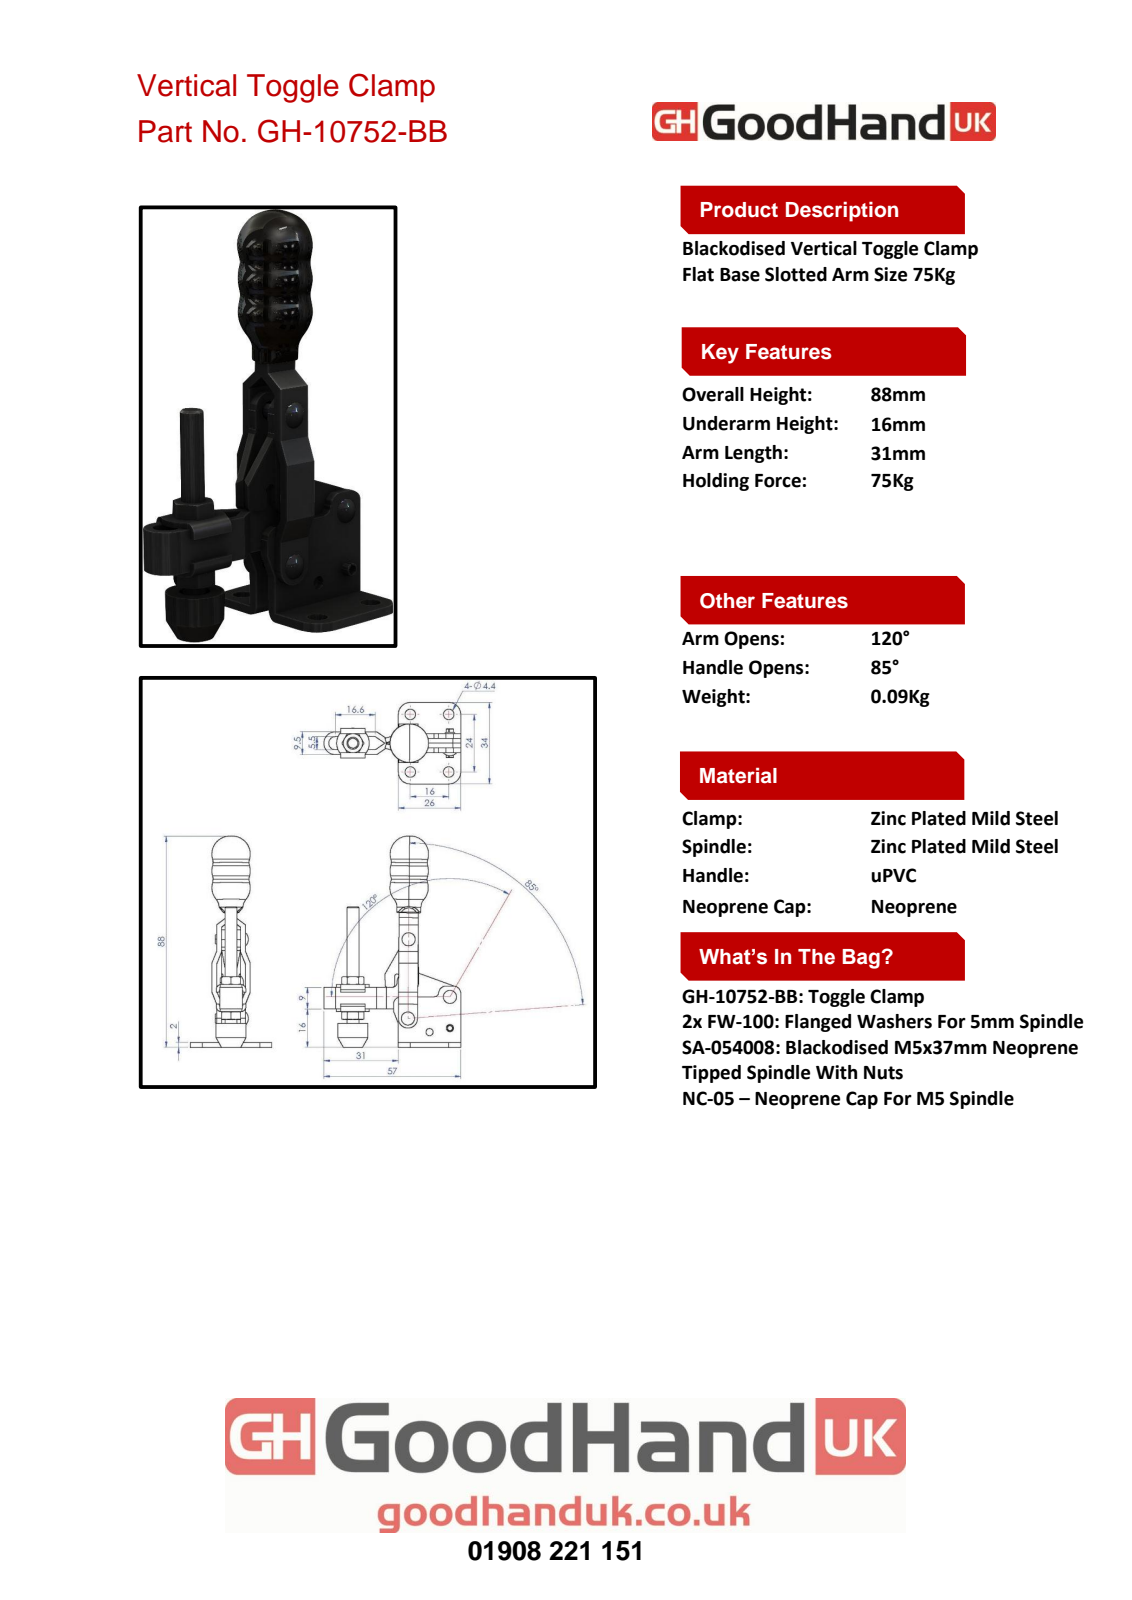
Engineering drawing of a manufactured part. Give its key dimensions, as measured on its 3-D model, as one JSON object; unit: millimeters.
{"part_name": "fw100; Revit-3.0-4_D3-L12; GH-10752-BB; 110752B13 (+8 more)", "step_written_by": "SolidWorks 2016 (AUTOMOTIVE_DESIGN)", "units": "millimeters", "bodies": {"solids": 18, "faces": 431, "planar": 168, "cylindrical": 151, "other": 112}, "overall_size": [88.02, 57, 34], "volume_mm3": 13569, "surface_area_mm2": 17590, "round_holes": [[2, 4], [4.05, 4], [4.4, 4], [3, 2], [4.1, 2], [2.1, 1], [4.2, 1], [5, 1], [6.5, 1], [9, 1]], "round_bosses_or_shafts": [[3, 4], [12.5, 1]], "partial_cylinders_radius": [[1, 10], [5, 7], [2, 4], [2.2, 4], [3, 4], [4, 4], [2.75, 1], [4.75, 1]], "face_to_face_distances": [2, 4, 6, 8, 10, 1.25, 8.75, 0.75, 2.75, 4.75], "hole_center_spacings": [16, 24, 26.74, 28.84, 41.67, 8.66, 10.63, 13]}
